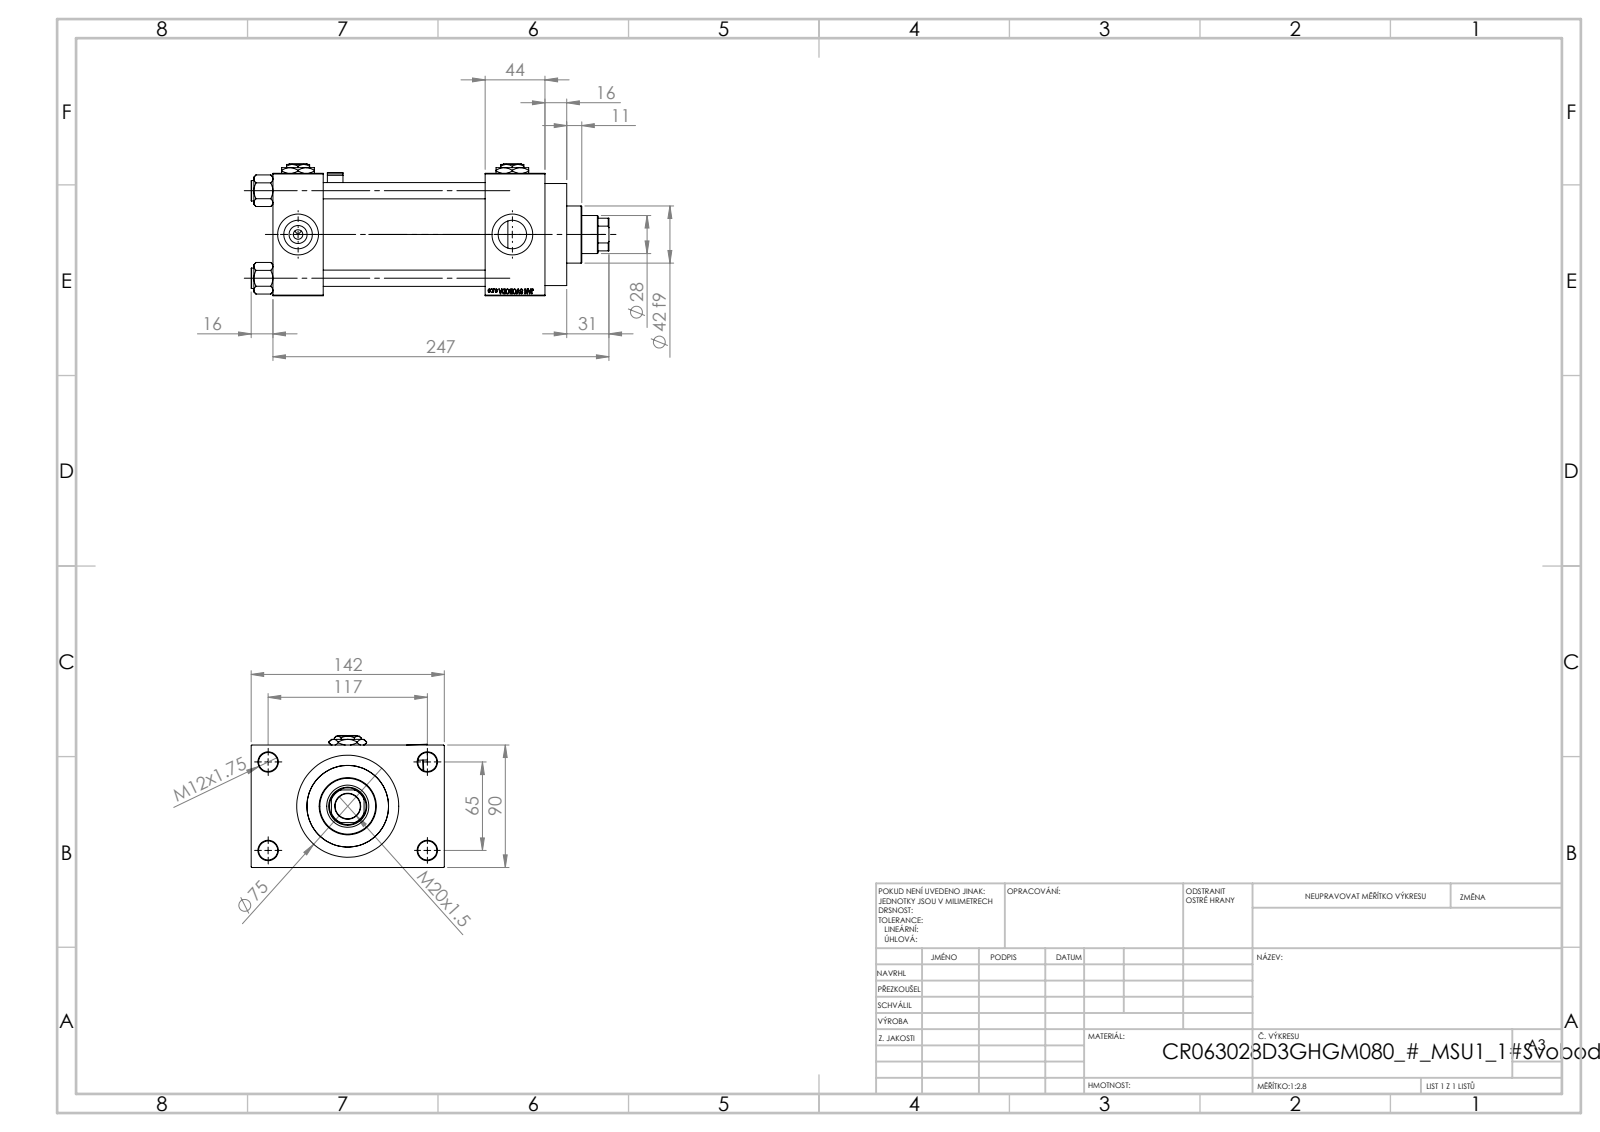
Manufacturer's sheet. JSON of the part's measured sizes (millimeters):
{"part_name": "V215CR_D_Body; V215CR_VCP_D; V215_VC_A; Zatka_pro_OIL_PORT (+3 more)", "step_written_by": "SolidWorks 2019 (CONFIG_CONTROL_DESIGN)", "units": "millimeters", "bodies": {"solids": 14, "faces": 1281, "planar": 574, "cylindrical": 129, "other": 578}, "overall_size": [263, 142, 97], "volume_mm3": 1213000, "surface_area_mm2": 250283, "round_holes": [[12, 4], [14, 4], [20.96, 4], [30, 4], [7, 3], [18.5, 1], [28, 1], [31, 1], [50, 1], [60, 1], [63, 1]], "round_bosses_or_shafts": [[15, 4], [75, 1], [69, 1], [42, 1], [6, 1]], "partial_cylinders_radius": [[0.5, 24], [1, 1], [2.5, 1], [4, 1], [13.5, 1]], "face_to_face_distances": [90, 119, 37, 156, 163, 200, 44, 26, 116, 16], "hole_center_spacings": [26.35, 45.47, 64.3, 66.92, 69.81, 90.65, 111.34, 65]}
